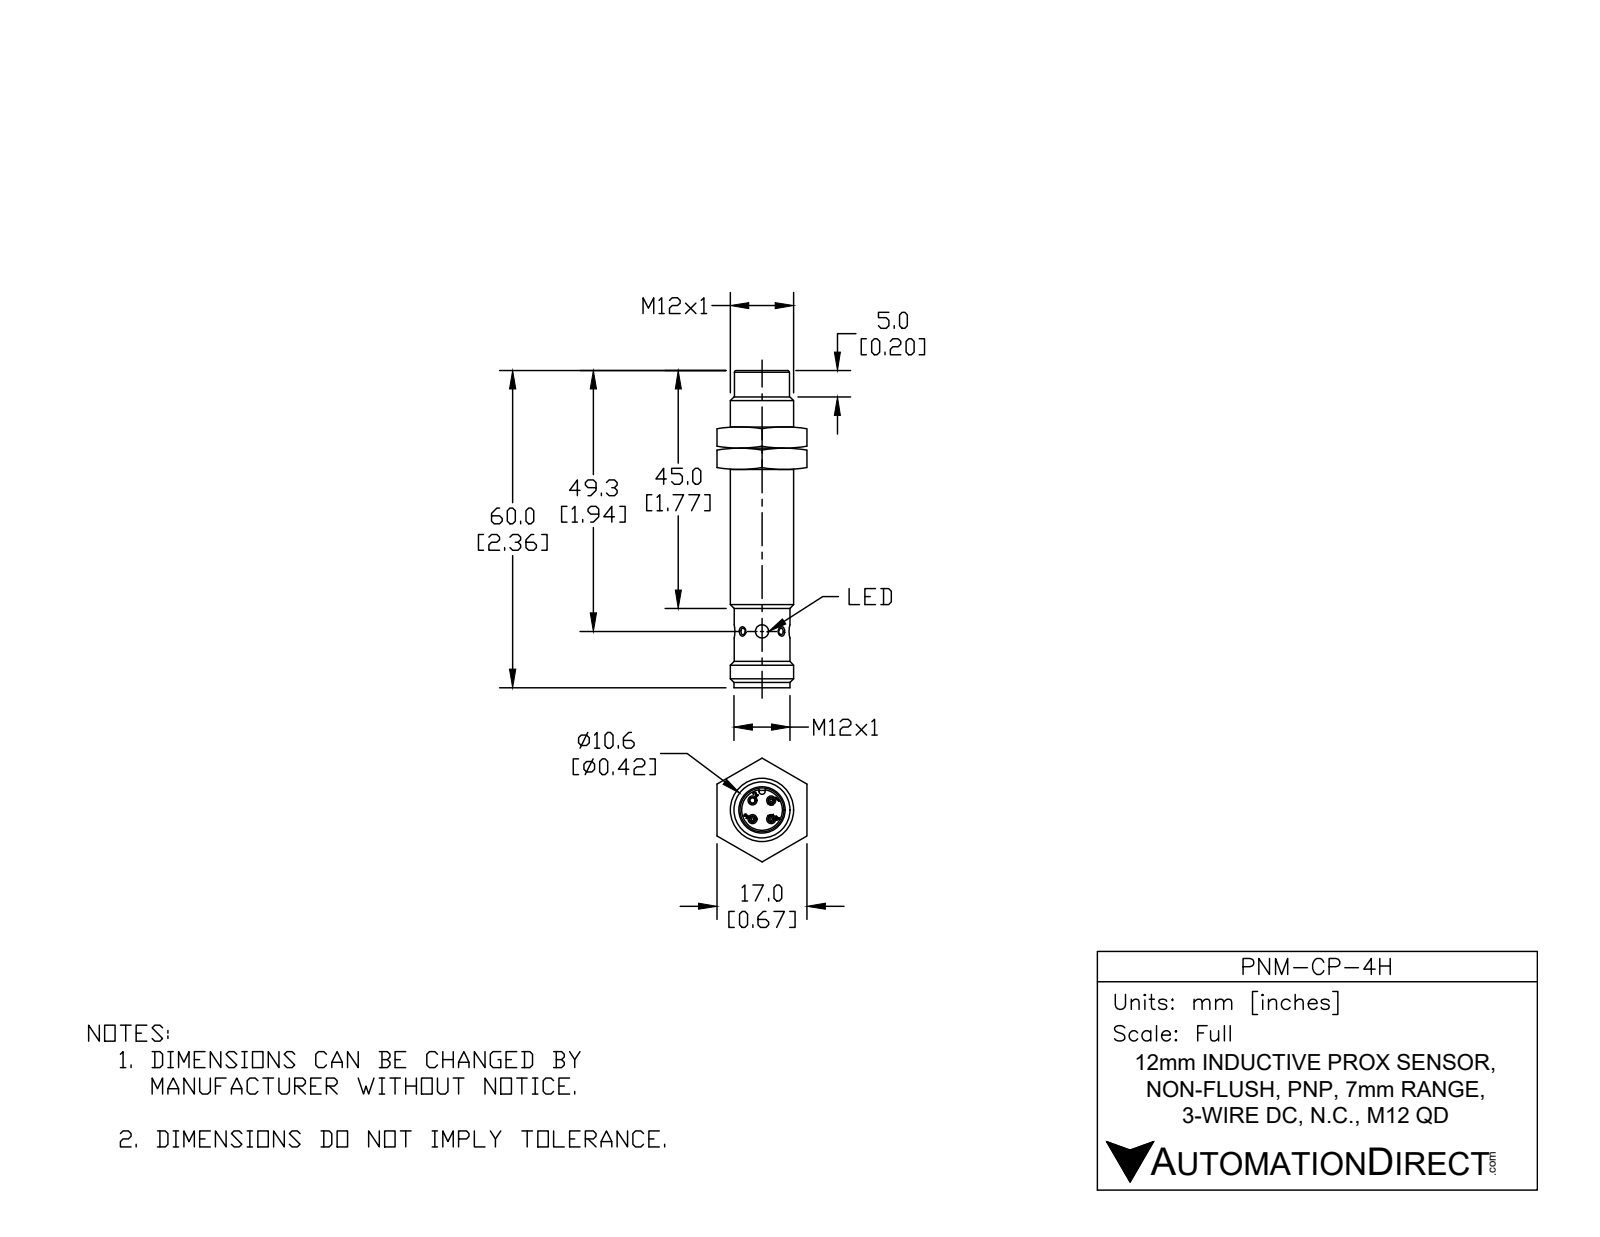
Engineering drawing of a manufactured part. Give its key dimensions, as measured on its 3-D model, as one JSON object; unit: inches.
{"part_name": "PNM-CP-4H", "step_written_by": "SolidWorks 2017 (AUTOMOTIVE_DESIGN)", "units": "inches", "bodies": {"solids": 1, "faces": 479, "planar": 119, "cylindrical": 134, "other": 226}, "overall_size": [2.362, 0.472, 0.472], "volume_in3": 0.35, "surface_area_in2": 10.25, "round_holes": [[0.043, 3], [0.04, 2], [0.098, 2], [0.038, 1], [0.04, 1], [0.327, 1], [0.394, 1], [0.401, 1]], "round_bosses_or_shafts": [[0.039, 9], [0.472, 1], [0.417, 1], [0.415, 1], [0.4, 1], [0.392, 1], [0.39, 1], [0.376, 1]], "partial_cylinders_radius": [[0.004, 36], [0.024, 1], [0.031, 1], [0.161, 1]], "face_to_face_distances": [0.039, 1.87, 1.831, 0.018, 0.022, 1.852, 2.323, 0.142, 2.012, 1.994], "hole_center_spacings": [0.098, 0.139, 0.197]}
